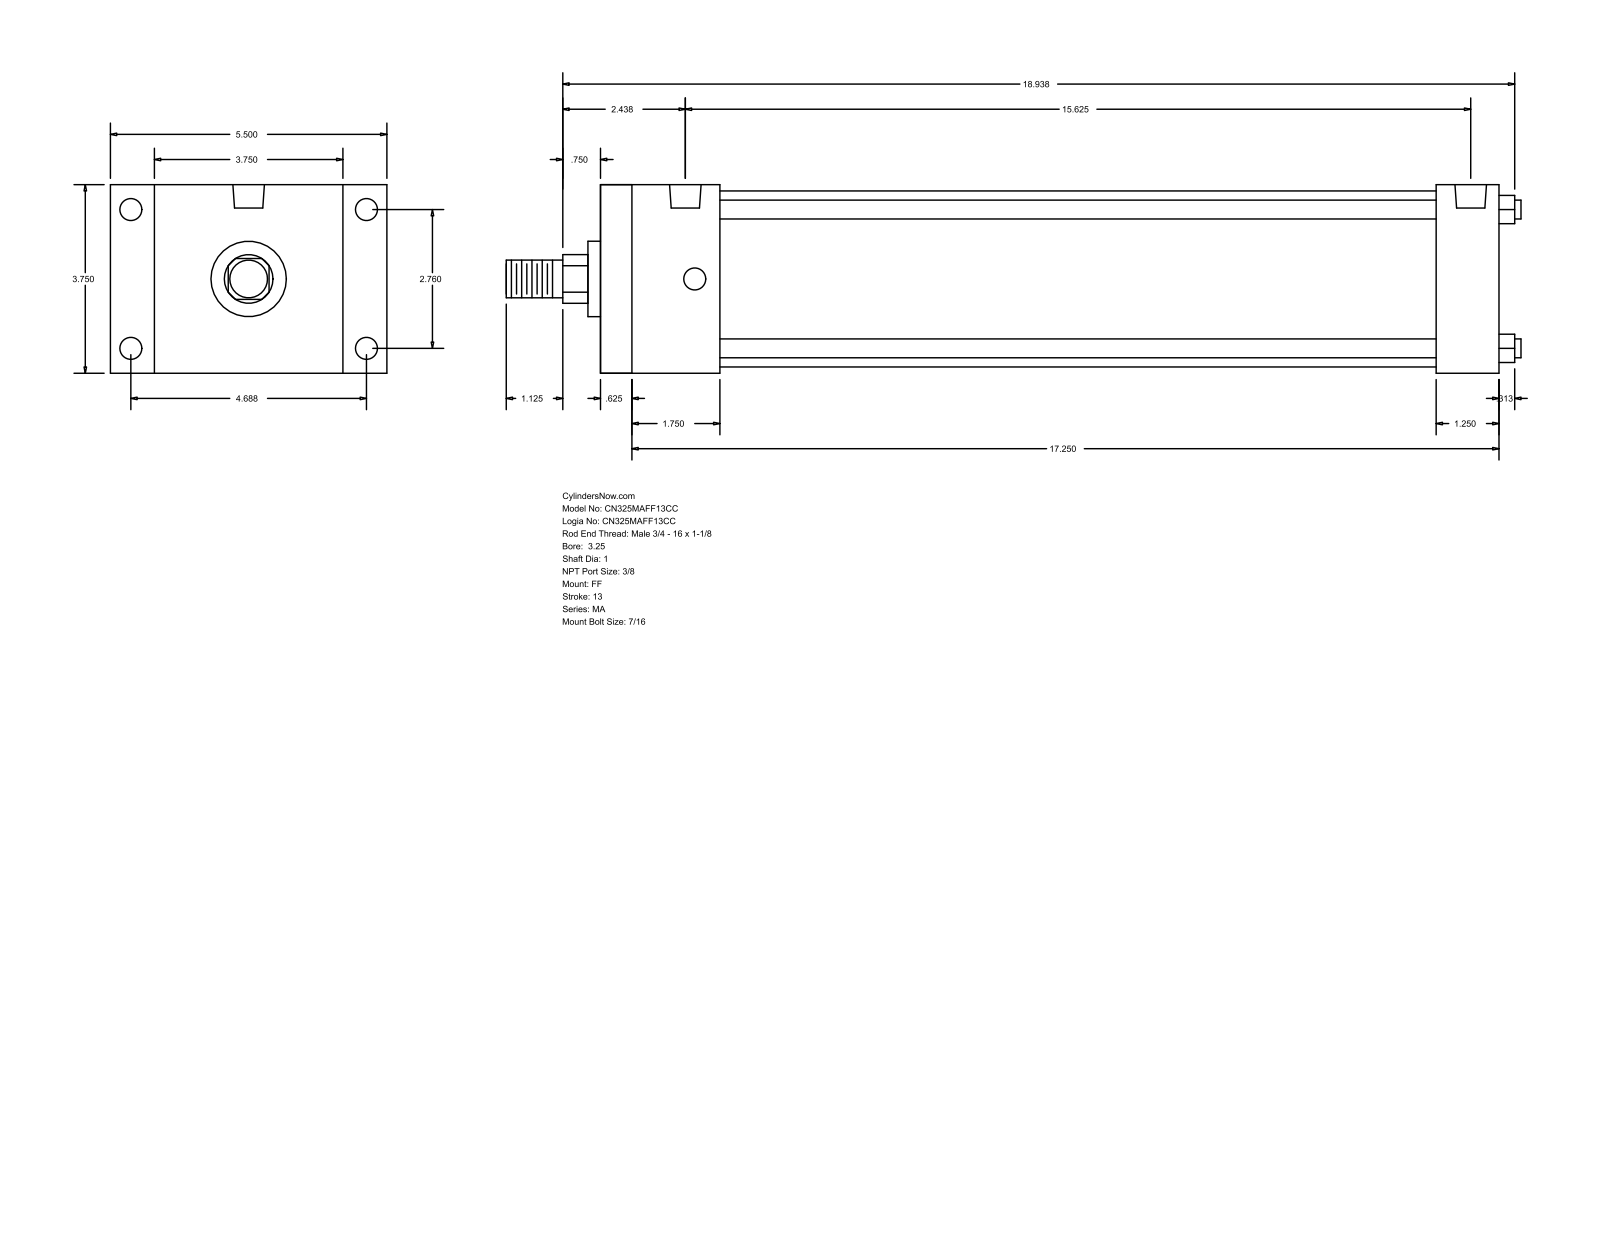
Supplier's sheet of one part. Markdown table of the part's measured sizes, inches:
| quantity | value |
| --- | --- |
| part name | MA_FF__0325_1 |
| STEP written by | GSSL Pune (CONFIG_CONTROL_DESIGN) |
| units | inches |
| bodies | 0 solids, 92 faces (64 planar, 28 cylindrical, 0 other) |
| overall size | 20.187 × 5.5 × 3.75 |
| round holes (diameter × count) | 0.437 × 8, 0.627 × 2 |
| round bosses / shafts (diameter × count) | 0.375 × 4, 3.5 × 1, 1.5 × 1, 1 × 1, 0.75 × 1 |
| partial cylindrical surfaces (radius × count) | 0.484 × 1 |
| main face-to-face distances | 3.75, 17.875, 0.625, 17.25, 0.875, 4.625, 2.375, 16.625, 1.75, 16 |
| hole center spacings | 2.76, 4.687, 5.439, 15.25, 0.187, 0.188, 15.437, 15.438 |
